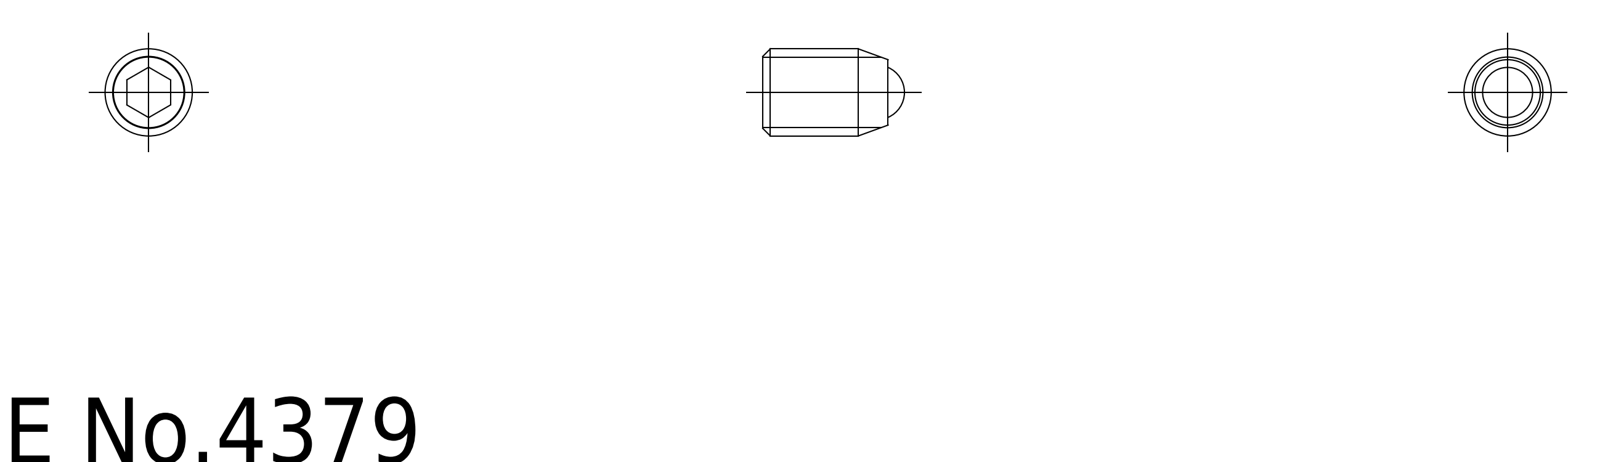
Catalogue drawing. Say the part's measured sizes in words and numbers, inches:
The part is named "ball; SCS_M4_6_R_17012_36". Its 3-D file was written by "CADfix (AUTOMOTIVE_DESIGN)". It is 2 solids with 20 faces: 0 planar, 0 cylindrical and 20 other. Overall it measures 0.256 by 0.157 by 0.157 inches. Its volume is 0.003 cubic inches and its surface area 0.223 square inches.
